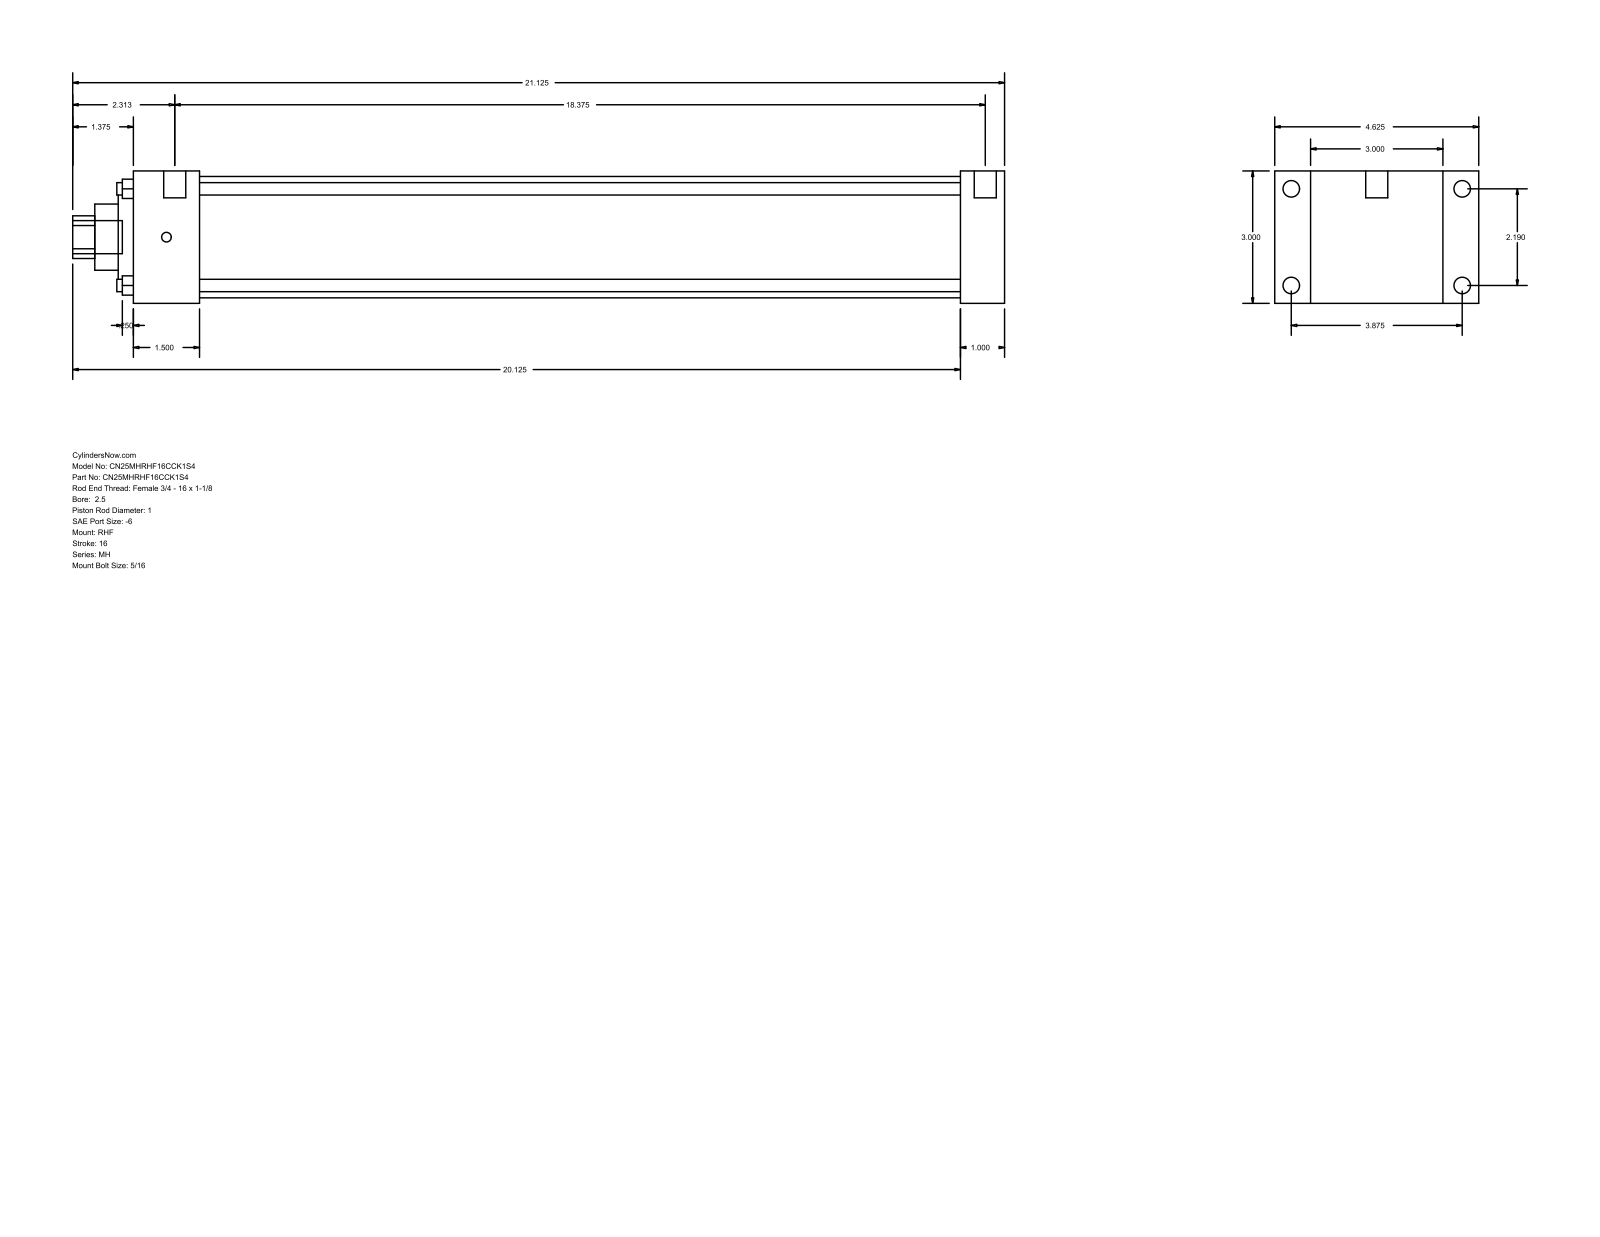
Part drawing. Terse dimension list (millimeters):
name: MH_RHF__0250_1
written by: GSSL Pune (CONFIG_CONTROL_DESIGN)
unit: mm
bodies: 0 solids, 90 faces (61 planar, 29 cylindrical, 0 other)
size: 536.58 × 117.47 × 76.2
holes: 4× ⌀7.14, 1× ⌀25.4, 1× ⌀38.1, 1× ⌀60.33, 1× ⌀69.85
bosses: 4× ⌀9.53, 4× ⌀5.56, 2× ⌀12.7, 1× ⌀19.05
rounds: 1× R12.29
face distances: 76.2, 25.4, 20.64, 96.84, 476.26, 501.66, 117.48, 38.11, 438.15, 463.55
hole spacings: 39.33, 55.62, 78.66
